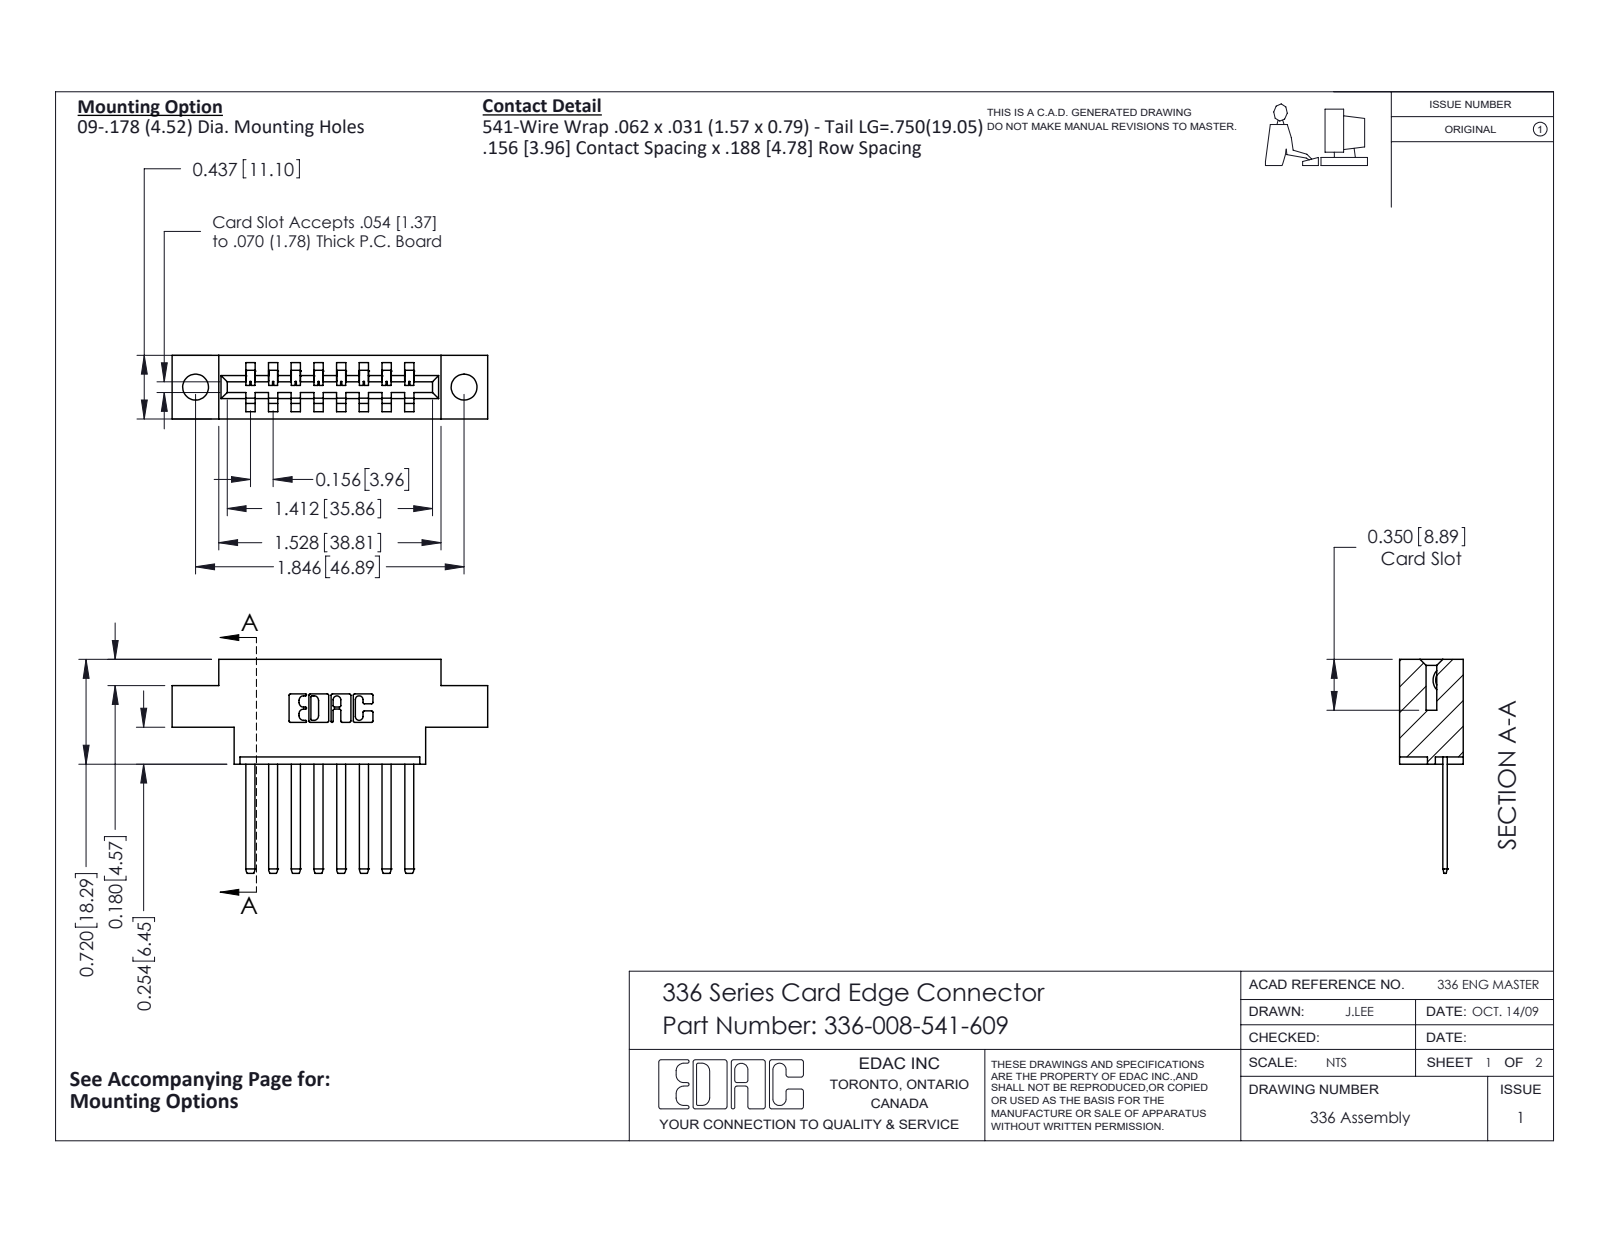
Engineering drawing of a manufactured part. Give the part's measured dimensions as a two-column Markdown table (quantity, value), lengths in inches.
| quantity | value |
| --- | --- |
| part name | 336 Part_Offset - .178 Dia - TH; 336-290-001_336-290-541; 336-008-541-609 |
| STEP written by | SolidWorks 2020 (CONFIG_CONTROL_DESIGN) |
| units | inches |
| bodies | 9 solids, 518 faces (346 planar, 172 cylindrical, 0 other) |
| overall size | 2.169 × 1.47 × 0.437 |
| volume | 0.421 in³ |
| surface area | 10.89 in² |
| round holes (diameter × count) | 0.178 × 2 |
| partial cylindrical surfaces (radius × count) | 0.01 × 22, 0.004 × 16, 0.056 × 16, 0.007 × 6, 0.031 × 6, 0.026 × 3, 0.022 × 2, 0.04 × 2 |
| main face-to-face distances | 0.156, 0.437, 0.468, 0.624, 0.312, 0.312, 0.22, 0.181, 0.376, 0.78 |
| hole center spacings | 1.846 |
